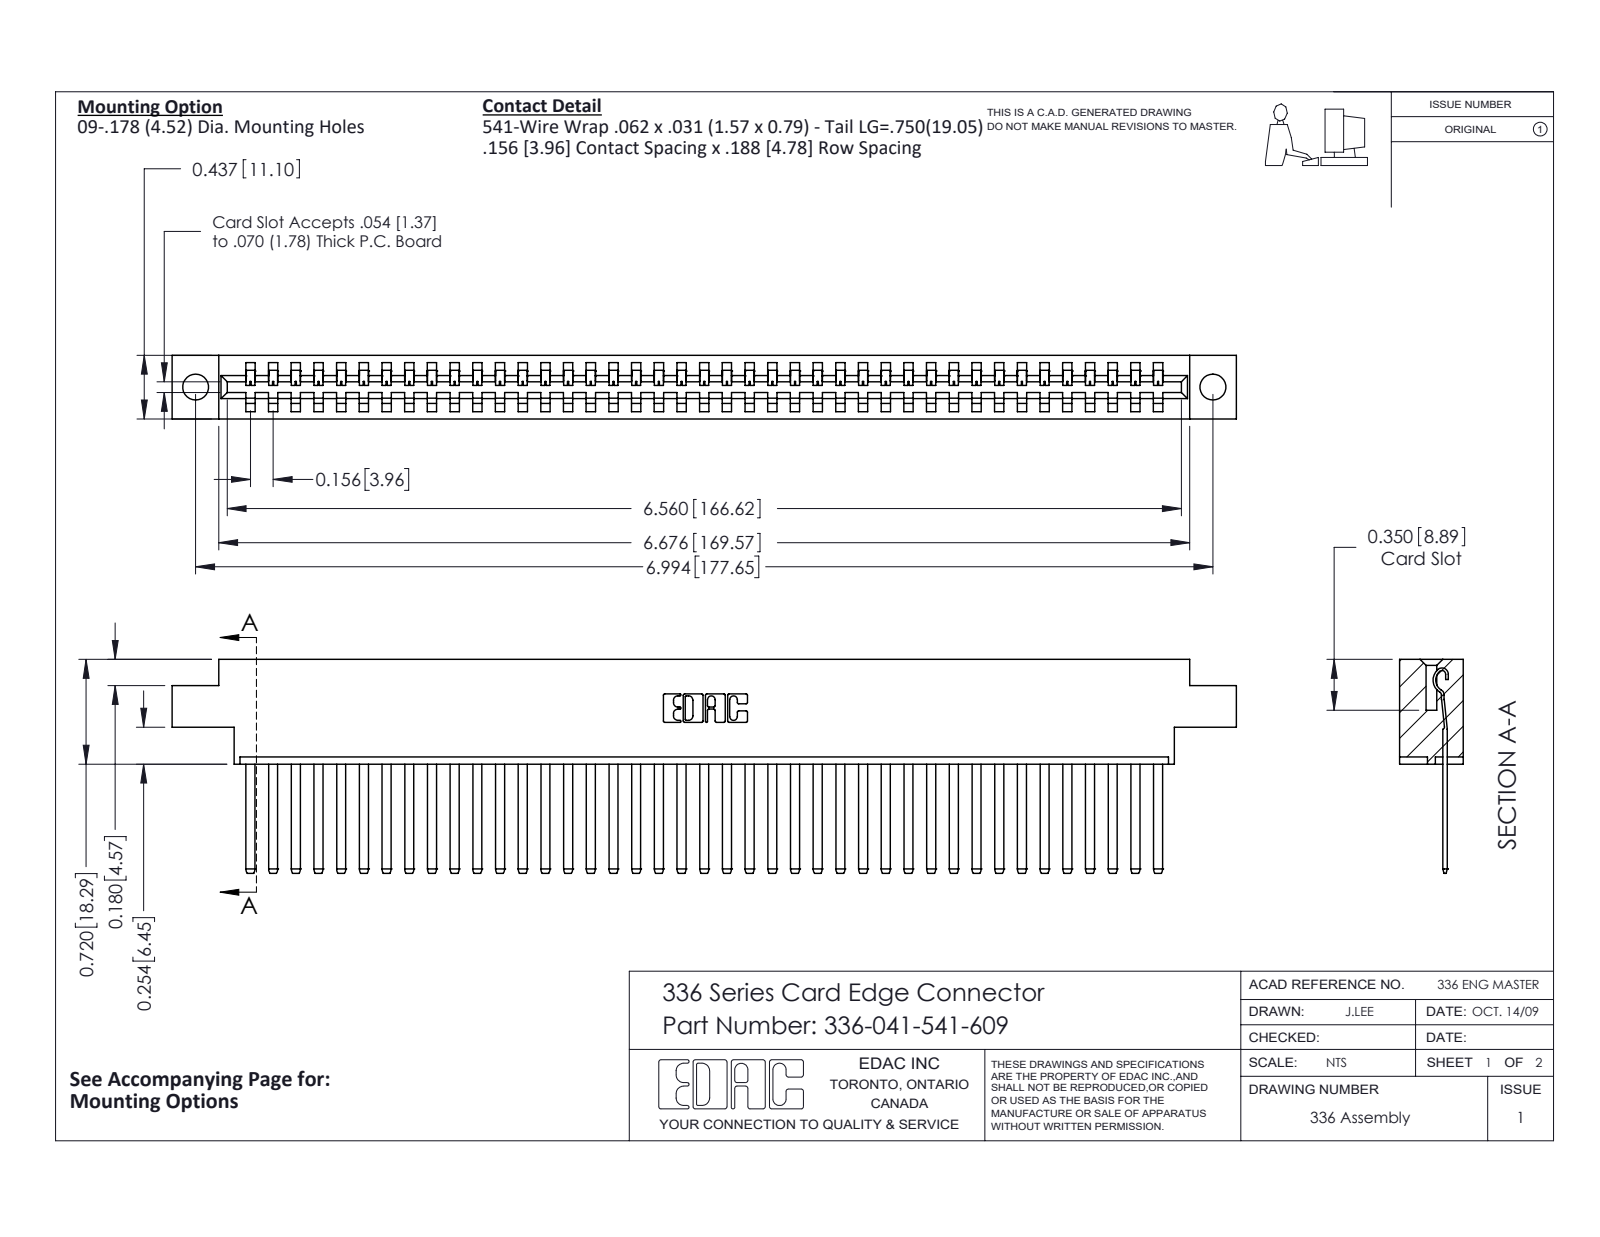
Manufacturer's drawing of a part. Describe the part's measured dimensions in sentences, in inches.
The part is named "336-041-541-609; 336 Part_Offset - .178 Dia - TH; 336-290-001_336-290-541". Its 3-D file was written by "SolidWorks 2020 (CONFIG_CONTROL_DESIGN)". It is 42 solids with 2168 faces: 1468 planar, 700 cylindrical and 0 other. Overall it measures 7.317 by 1.47 by 0.437 inches. Its volume is 1.642 cubic inches and its surface area 45.3 square inches. Round holes: 2 of diameter 0.178. Partial cylindrical surfaces (rounded edges, fillets, slot ends): 82 of radius 0.004, 82 of radius 0.056, 22 of radius 0.01, 6 of radius 0.007, 6 of radius 0.031, 3 of radius 0.026, 2 of radius 0.022, 2 of radius 0.04. The main face-to-face distances are 0.437, 0.181, 0.328, 0.14, 0.297, 0.109, 0.031, 0.256, 0.05, 0.387. The hole center spacings are 6.994.
